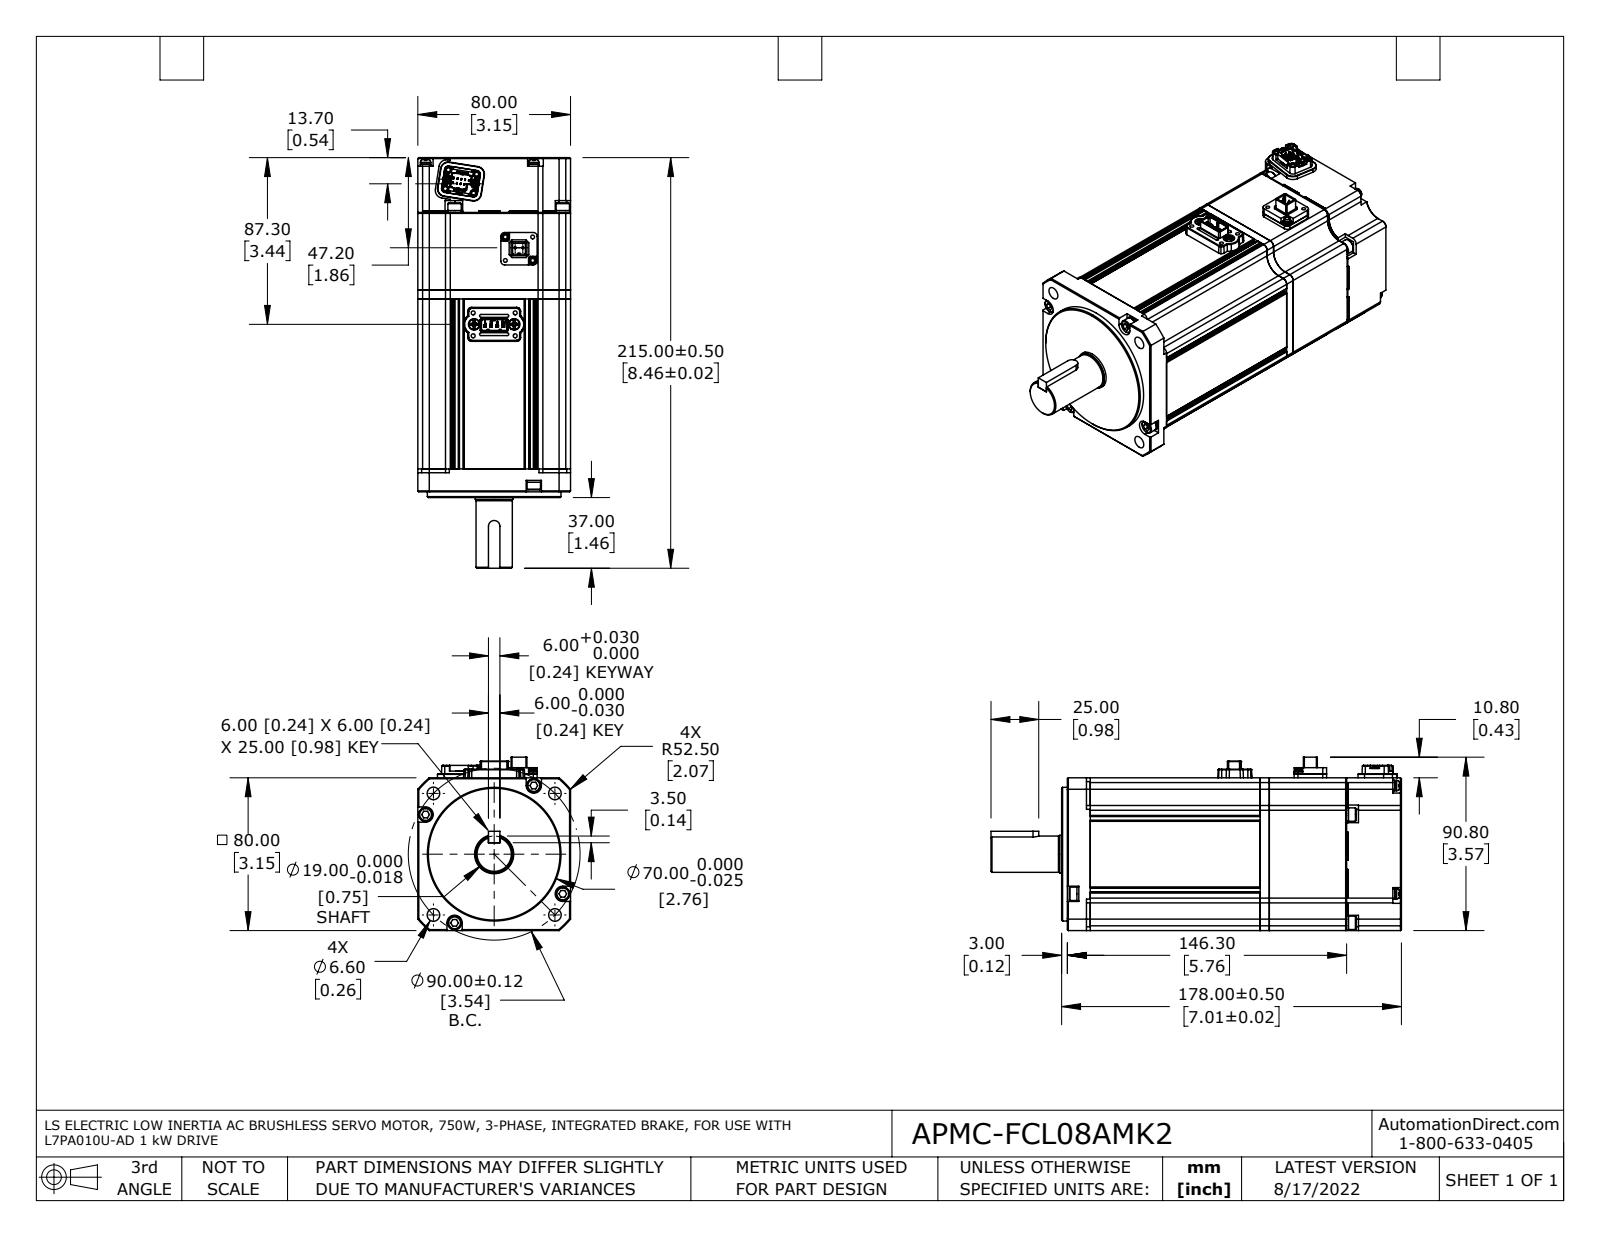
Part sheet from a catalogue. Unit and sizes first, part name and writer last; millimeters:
Units: millimetres
Overall size (bounding box): 215 × 90.8 × 80
Round holes (diameter × count): ⌀2.1 ×10, ⌀4 ×8, ⌀4.5 ×8, ⌀2 ×6, ⌀3 ×6, ⌀3.5 ×4, ⌀6.6 ×4, ⌀1 ×2, ⌀6 ×2, ⌀3.3 ×1, ⌀3.4 ×1, ⌀13 ×1
Round bosses / shafts (diameter × count): ⌀7.2 ×8, ⌀7 ×8, ⌀5.4 ×6, ⌀4.2 ×2, ⌀3.6 ×2, ⌀3.5 ×2, ⌀2.2 ×2, ⌀0.9 ×2
Partial cylindrical surfaces — rounded edges, fillets, slot ends (radius × count): R0.3 ×36, R0.2 ×20, R2 ×12, R1 ×10, R0.2 ×9, R2.5 ×9, R0.5 ×7, R4 ×7
Main face-to-face distances: 80, 93.8, 4.8, 89, 46, 40.5, 45.3, 134.3, 0.7, 41.2
Hole centre spacings: 41.5, 11.8, 52.7, 58.7, 68.7, 85.8, 6, 9.4
Volume: 1 005 000 mm³ · Surface area: 149 500 mm²
Bodies: 50 solids, 2079 faces (1312 planar, 562 cylindrical, 205 other)
Part name (STEP PRODUCT): SLM08GA003G03_Out Line(APMC-FCL08AMK2)(Ver.1.2) r1 nc fxt
STEP written by: SolidWorks 2017 (AUTOMOTIVE_DESIGN)
